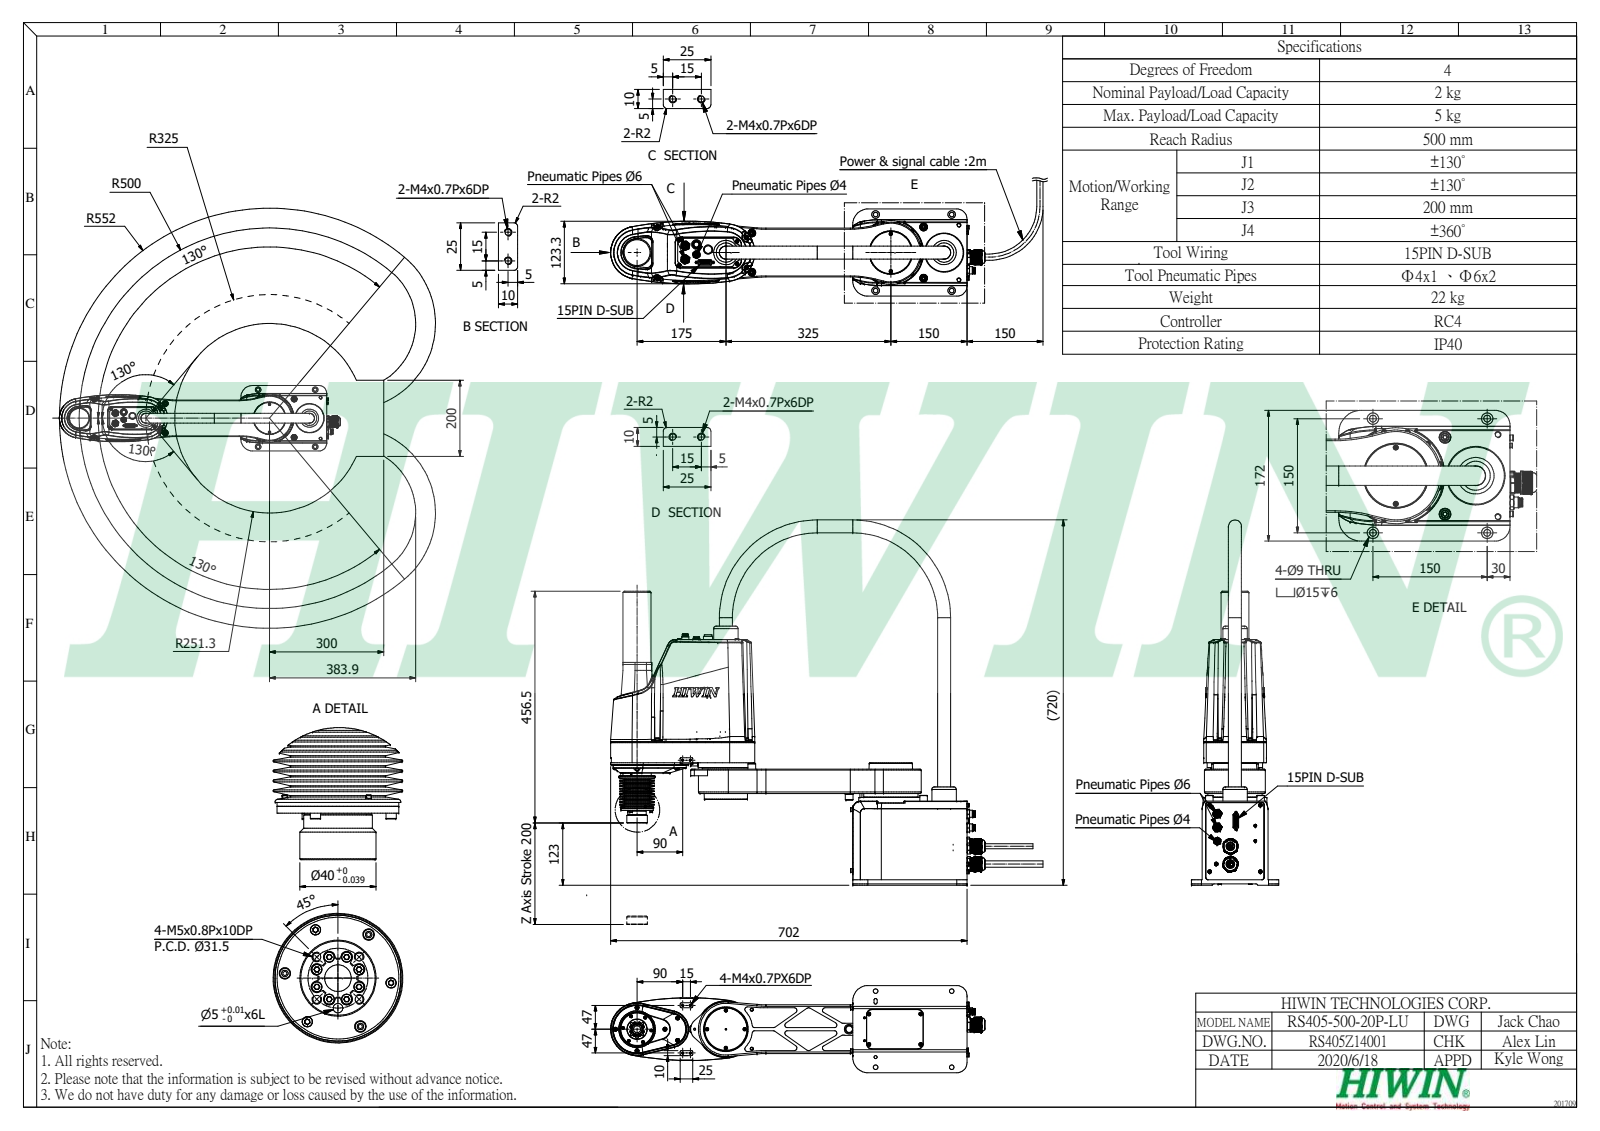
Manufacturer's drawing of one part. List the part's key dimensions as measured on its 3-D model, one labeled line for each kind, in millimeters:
Part name (STEP PRODUCT): RS405-500-20P-LU; RS405-1; A; B-500 (+3 more)
STEP written by: Autodesk Inventor 2020 (AUTOMOTIVE_DESIGN)
Units: millimetres
Bodies: 103 solids, 2977 faces (1227 planar, 736 cylindrical, 1014 other)
Overall size (bounding box): 737.36 × 720 × 172
Volume: 16 000 000 mm³ · Surface area: 1 371 000 mm²
Round holes (diameter × count): ⌀4.5 ×20, ⌀8.5 ×20, ⌀3.4 ×19, ⌀3.24 ×18, ⌀6.5 ×18, ⌀2.46 ×15, ⌀4.13 ×12, ⌀3.5 ×10, ⌀15 ×6, ⌀6 ×5, ⌀2.11 ×4, ⌀4.2 ×4
Round bosses / shafts (diameter × count): ⌀5.5 ×36, ⌀4 ×23, ⌀7 ×21, ⌀5.4 ×16, ⌀3 ×16, ⌀10 ×8, ⌀12 ×7, ⌀15 ×6
Partial cylindrical surfaces — rounded edges, fillets, slot ends (radius × count): R5 ×29, R3 ×25, R2 ×23, R1 ×20, R1.57 ×16, R4 ×11, R0.25 ×8, R0.5 ×8
Main face-to-face distances: 3, 8, 32.5, 97.5, 11, 221, 12.5, 59, 53, 229
Hole centre spacings: 30.02, 41.6, 58, 82.02, 98, 100.45, 112.04, 17.02
